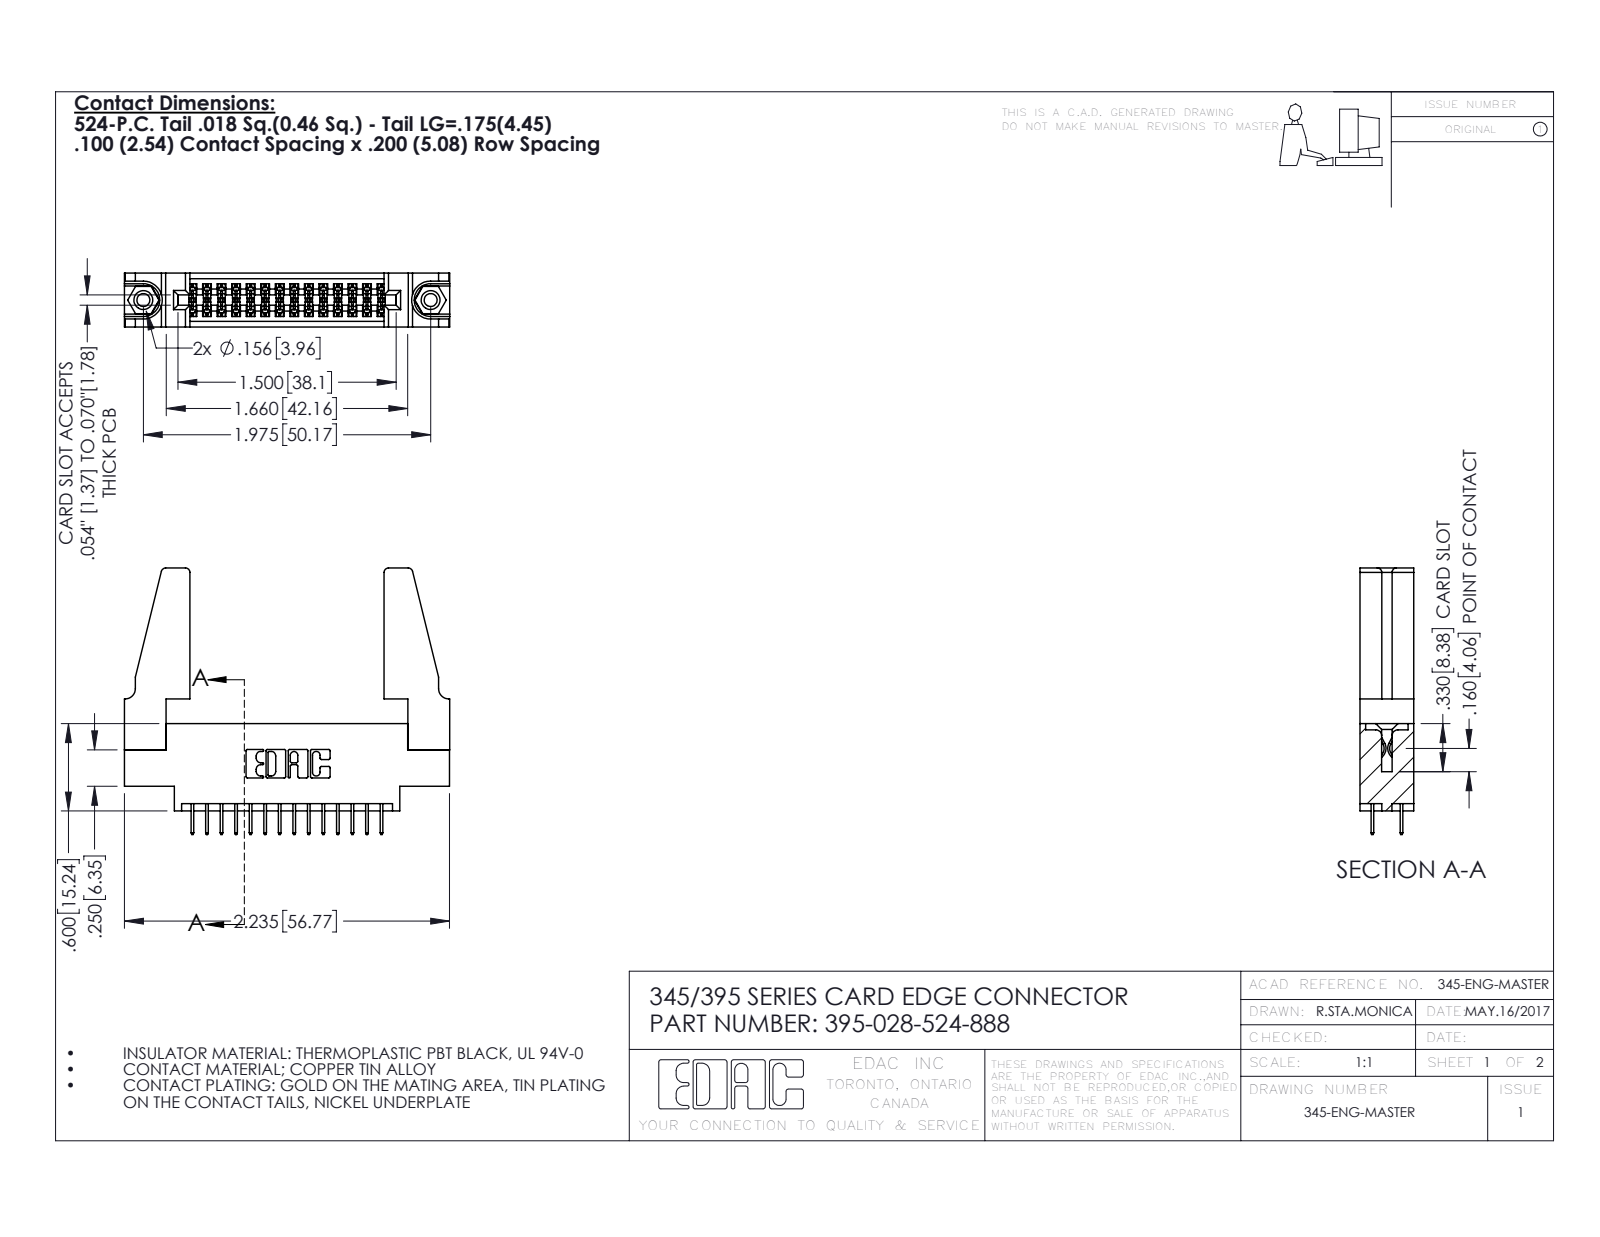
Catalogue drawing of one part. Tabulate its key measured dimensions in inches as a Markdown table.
| quantity | value |
| --- | --- |
| part name | 345-292-001_345-293-124; 395-028-524-888; 345-220-078_345-220-088; 345 Part_0.170 Offset - 0.156 Dia-TH (+1 more) |
| STEP written by | SolidWorks 2016 (CONFIG_CONTROL_DESIGN) |
| units | inches |
| bodies | 33 solids, 1766 faces (1248 planar, 502 cylindrical, 16 other) |
| overall size | 2.236 × 1.832 × 0.37 |
| volume | 0.51 in³ |
| surface area | 15.74 in² |
| round holes (diameter × count) | 0.089 × 2, 0.125 × 2, 0.156 × 2, 0.064 × 1 |
| round bosses / shafts (diameter × count) | 0.155 × 2 |
| partial cylindrical surfaces (radius × count) | 0.006 × 42, 0.01 × 22, 0.03 × 8, 0.007 × 6, 0.031 × 6, 0.026 × 3, 0.014 × 2, 0.019 × 2 |
| main face-to-face distances | 0.37, 0.072, 0.298, 0.2, 0.098, 0.272, 0.025, 0.225, 0.175, 0.148 |
| hole center spacings | 0.27, 1.742, 1.975 |
